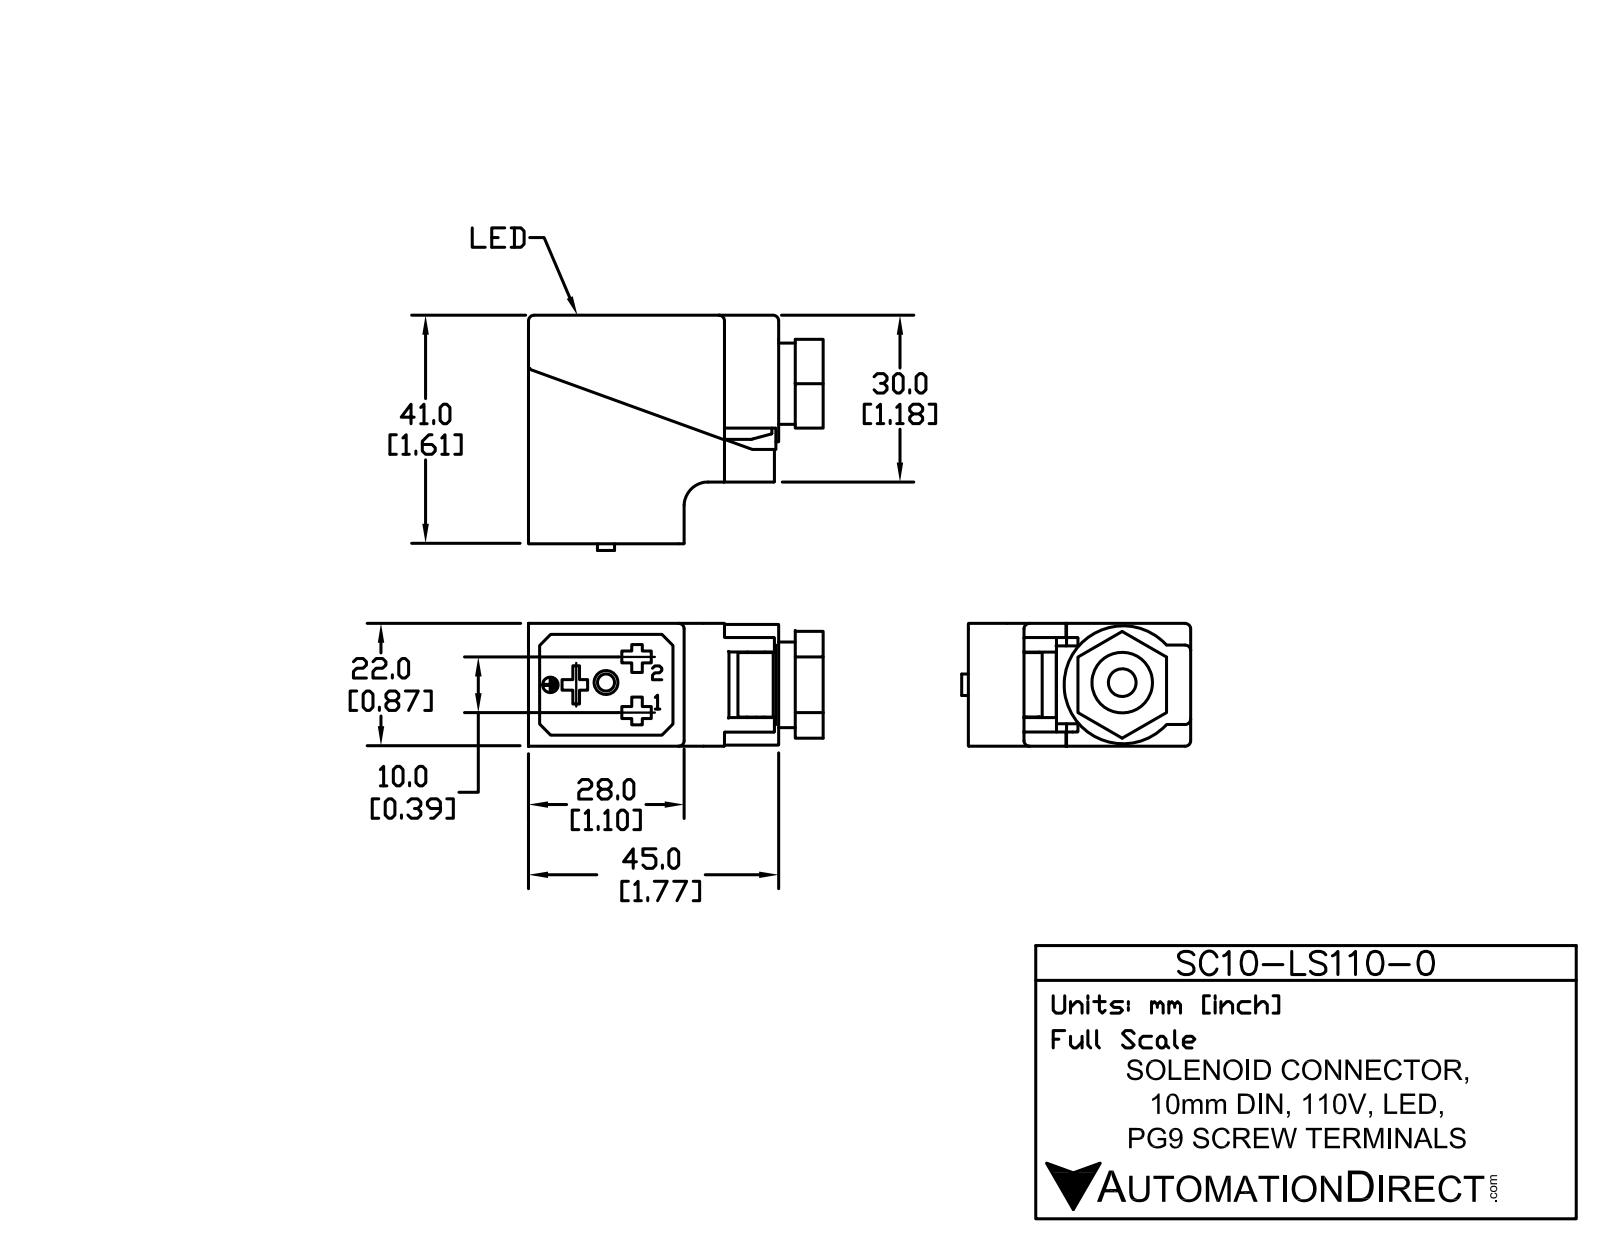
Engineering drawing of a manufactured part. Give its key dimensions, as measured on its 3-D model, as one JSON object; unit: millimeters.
{"part_name": "SC10-LS-110-0", "step_written_by": "SolidWorks 2011 (AUTOMOTIVE_DESIGN)", "units": "millimeters", "bodies": {"solids": 8, "faces": 512, "planar": 394, "cylindrical": 71, "other": 47}, "overall_size": [53.55, 46, 21.5], "volume_mm3": 23490, "surface_area_mm2": 18891, "round_holes": [[2.5, 1], [3, 1], [3.5, 1], [3.75, 1], [5.5, 1], [5.75, 1], [7, 1], [9.4, 1], [10, 1], [10.1, 1], [11, 1], [14, 1]], "round_bosses_or_shafts": [[1.5, 2], [15, 1], [13.5, 1], [13.4, 1], [11.7, 1], [5.9, 1], [3, 1], [2.9, 1]], "partial_cylinders_radius": [[1, 12], [2, 12], [0.36, 2], [1.5, 2], [0.5, 1], [1.36, 1], [1.43, 1], [1.5, 1]], "face_to_face_distances": [2.35, 16.8, 2, 2.3, 19.1, 19.15, 21.45, 21.15, 0.35, 21.1], "hole_center_spacings": [8.63, 8.88]}
